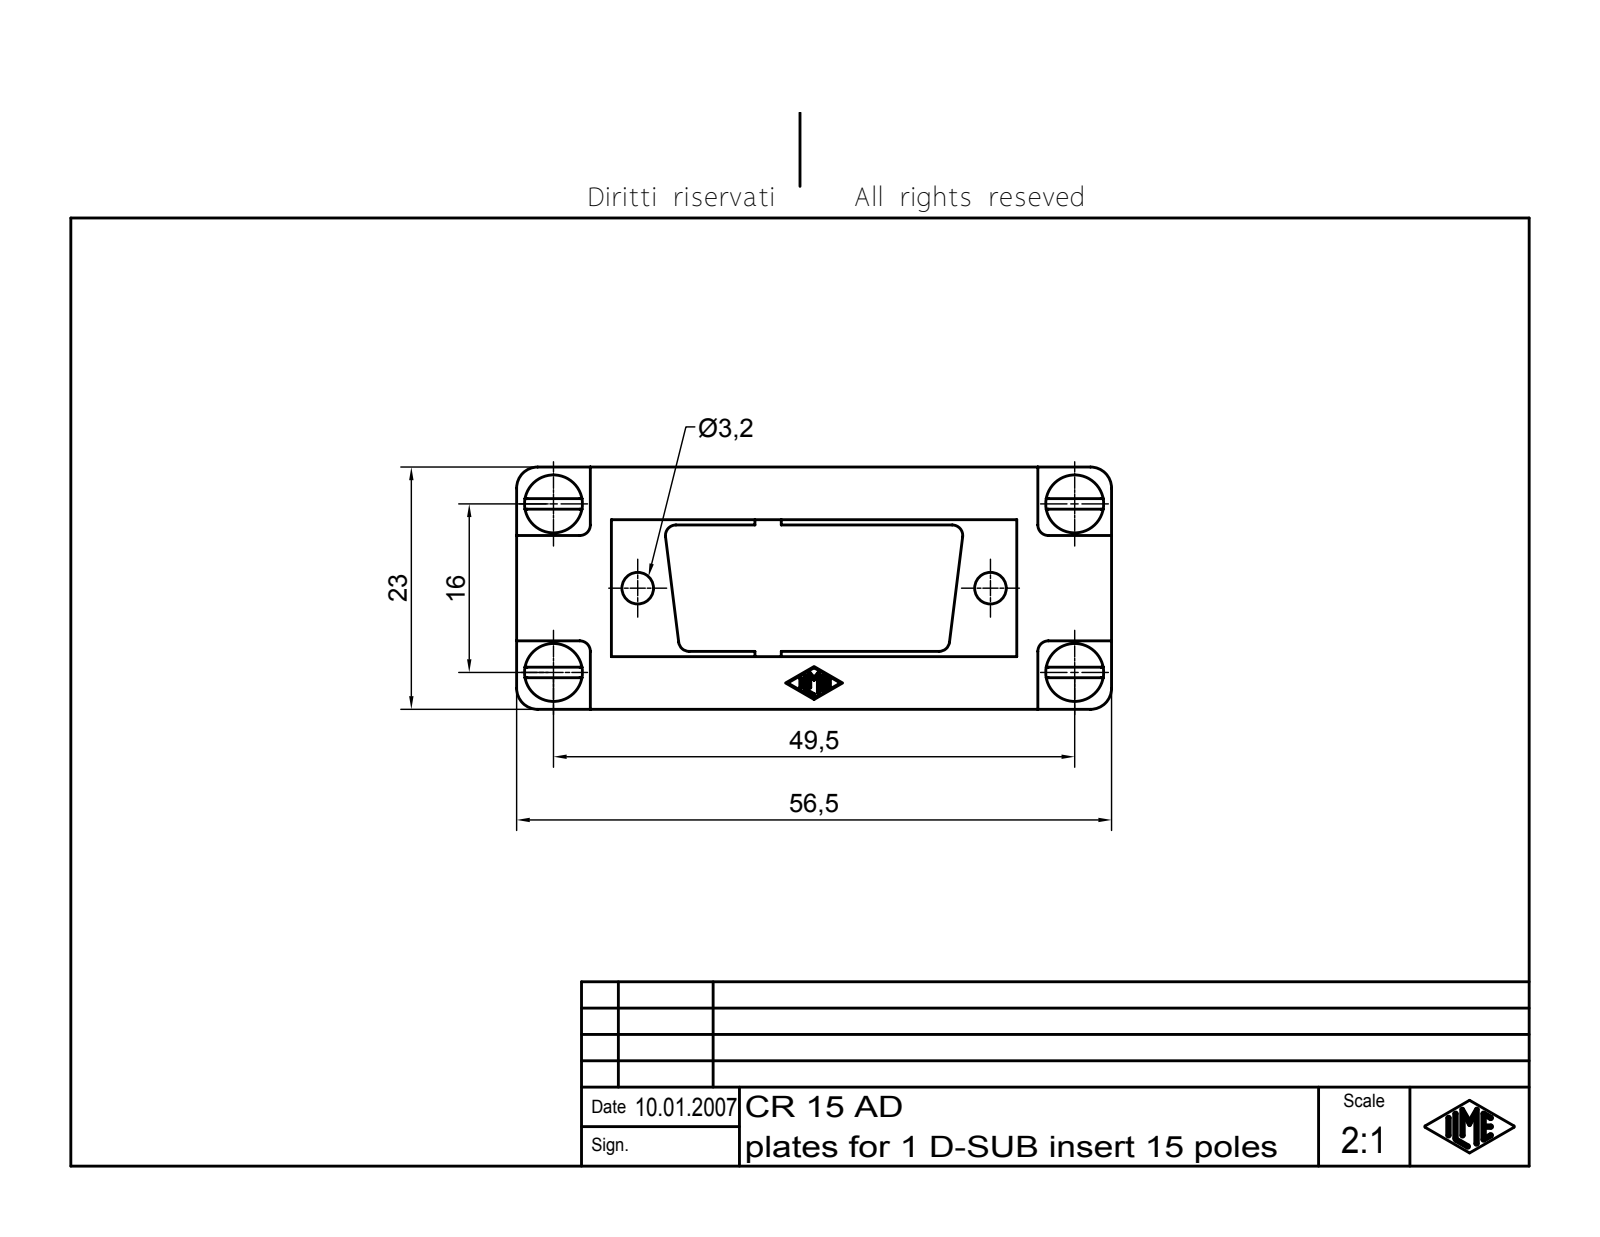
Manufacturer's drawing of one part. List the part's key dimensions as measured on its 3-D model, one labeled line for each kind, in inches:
Part name (STEP PRODUCT): CR 15 AD
STEP written by: Autodesk Inventor 7 (AUTOMOTIVE_DESIGN)
Units: inches
Bodies: 1 solid, 177 faces (101 planar, 52 cylindrical, 24 other)
Overall size (bounding box): 2.224 × 0.906 × 0.669
Volume: 0.418 in³ · Surface area: 7.339 in²
Round holes (diameter × count): ⌀0.126 ×4, ⌀0.118 ×2
Round bosses / shafts (diameter × count): ⌀0.217 ×4, ⌀0.118 ×4
Partial cylindrical surfaces — rounded edges, fillets, slot ends (radius × count): R0.004 ×14, R0.039 ×6, R0.079 ×4
Main face-to-face distances: 0.315, 0.906, 0.039, 0.217, 0.689, 0.079, 0.197, 0.276, 0.118, 0.472
Hole centre spacings: 0.445, 1.664, 0.63, 1.949, 2.048, 1.319
